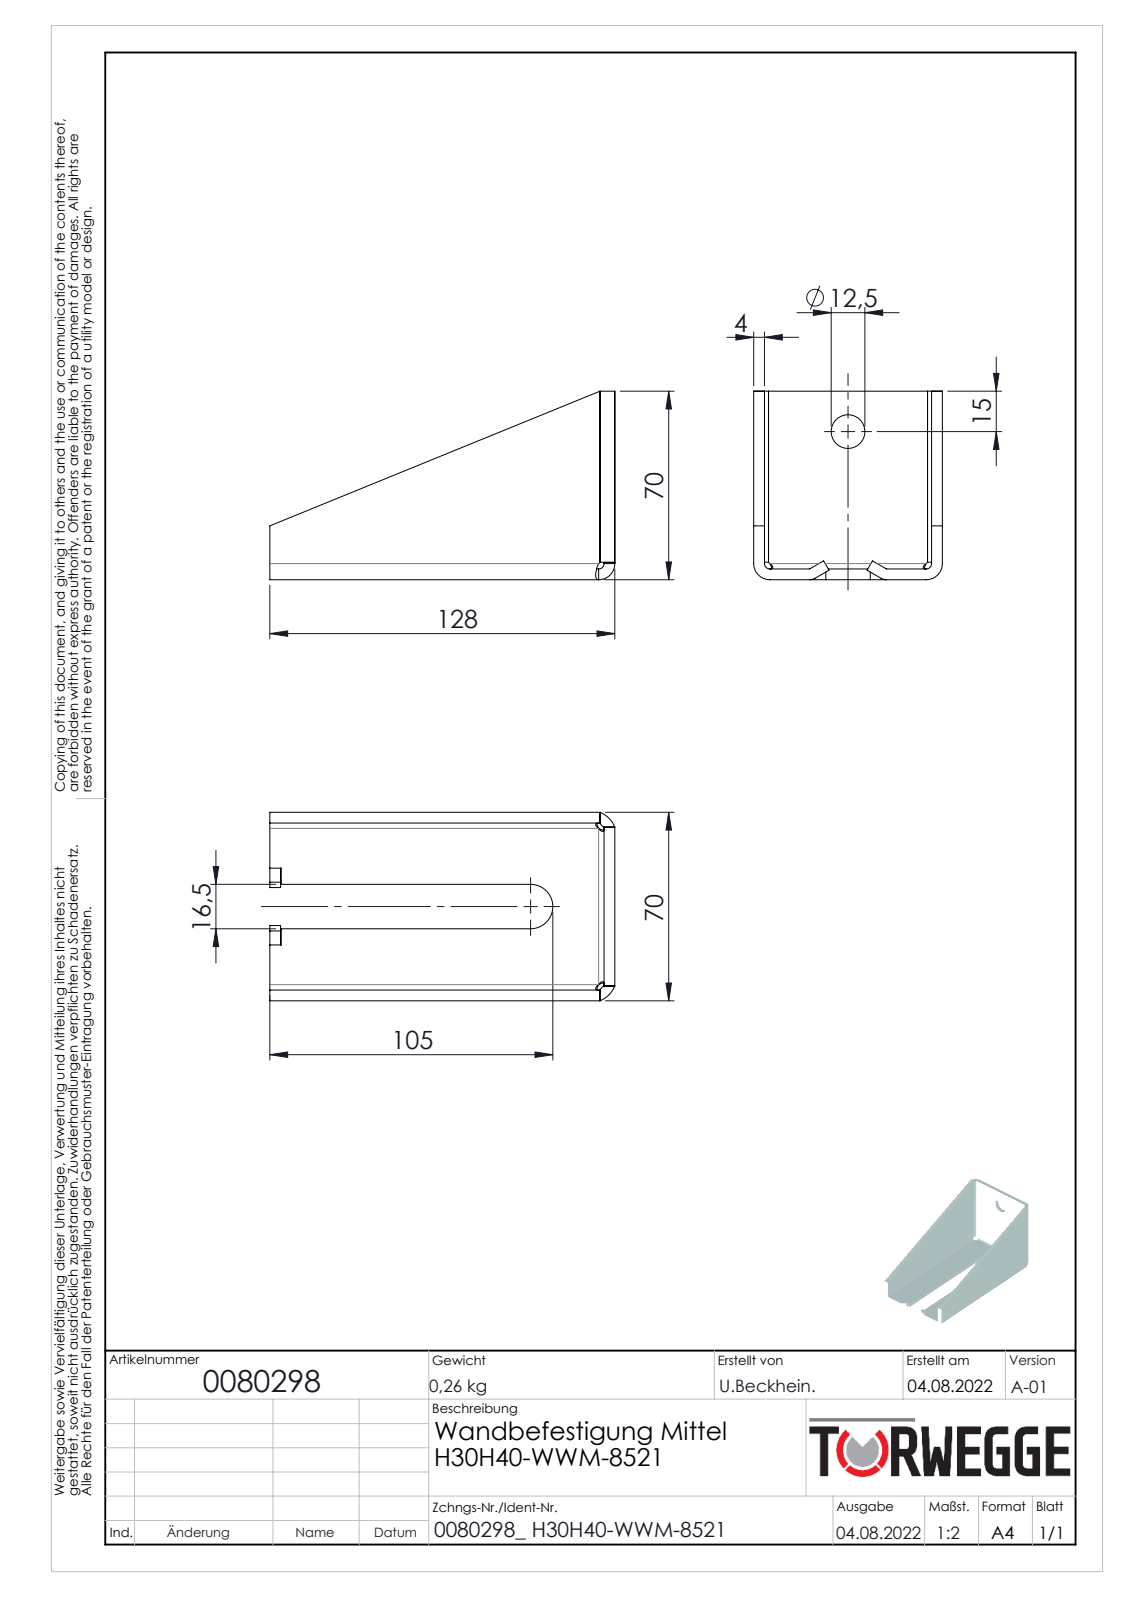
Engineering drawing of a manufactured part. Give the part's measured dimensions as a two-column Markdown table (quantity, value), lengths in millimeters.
| quantity | value |
| --- | --- |
| part name | 0080298 |
| STEP written by | SolidWorks 2020 (AUTOMOTIVE_DESIGN) |
| units | millimeters |
| bodies | 3 solids, 62 faces (39 planar, 19 cylindrical, 4 other) |
| overall size | 128 × 70 × 70 |
| volume | 84 197 mm³ |
| surface area | 47 217 mm² |
| round holes (diameter × count) | 12.5 × 1 |
| partial cylindrical surfaces (radius × count) | 2 × 3, 3.7 × 3, 6 × 3, 3 × 2, 4 × 2, 10 × 2, 8.25 × 1 |
| main face-to-face distances | 4, 66, 70, 62, 5.5, 1.5, 64.5, 60.5, 26.75, 43.25 |
